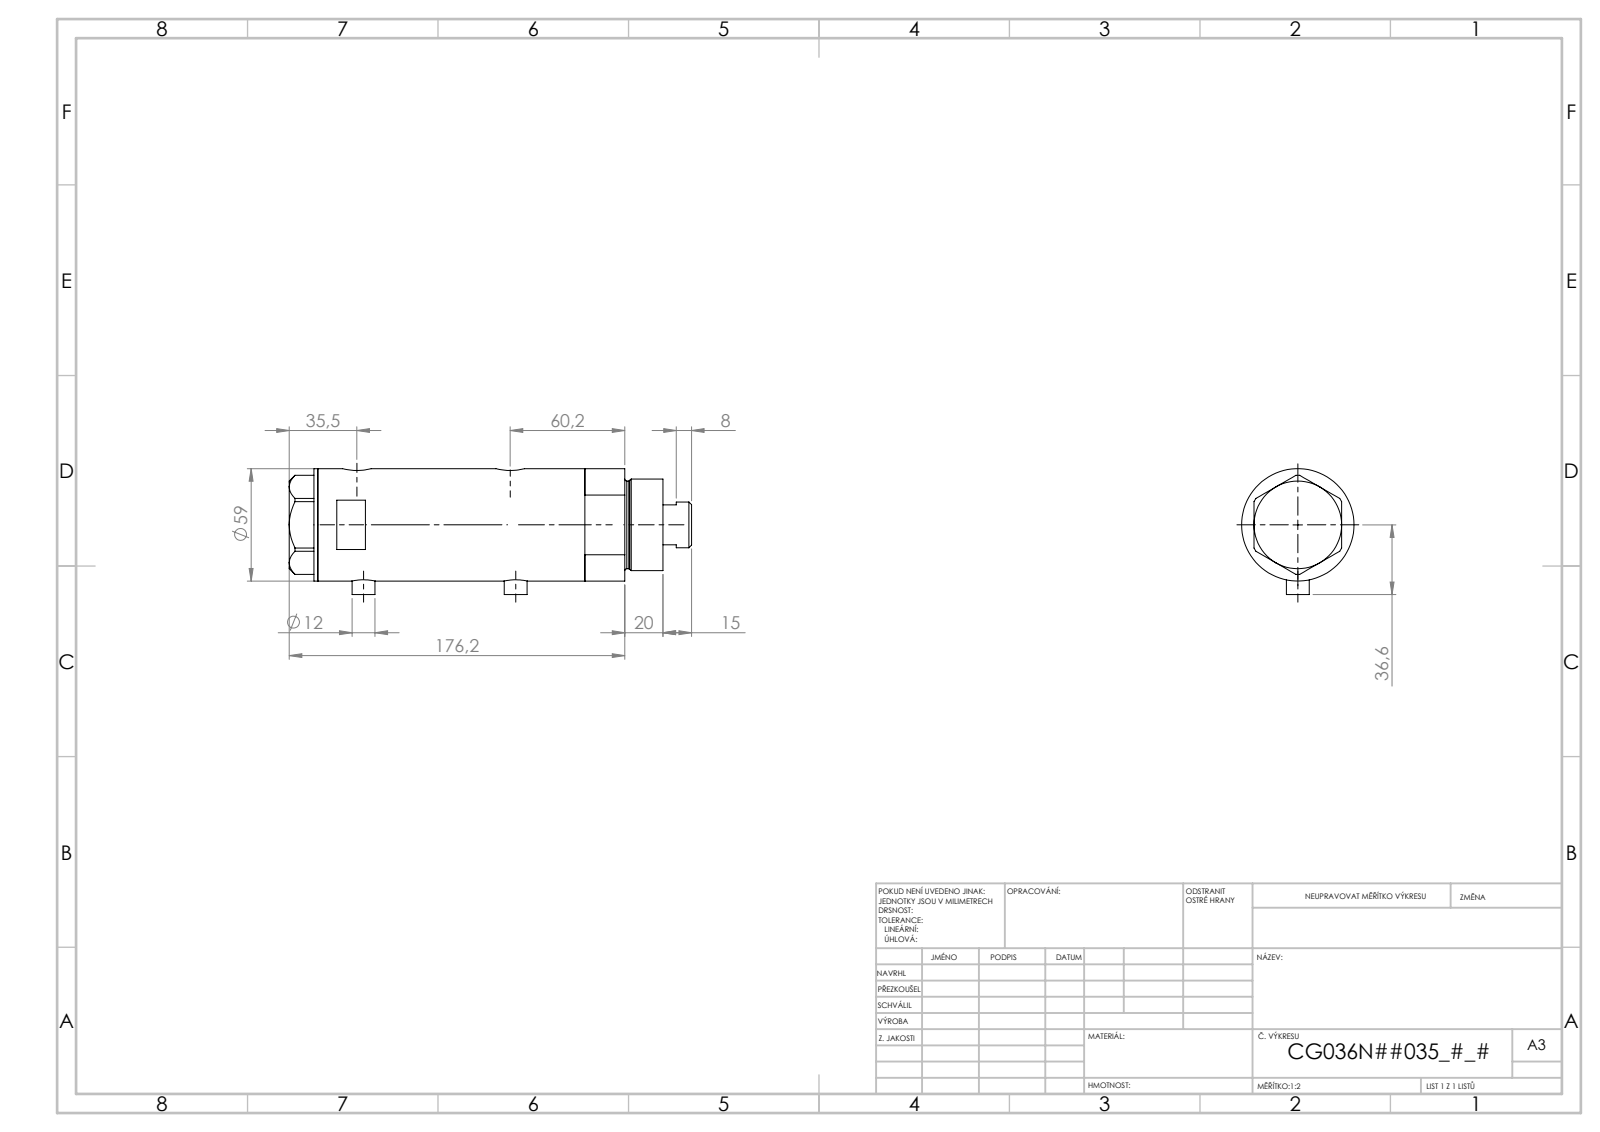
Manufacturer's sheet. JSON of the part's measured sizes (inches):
{"part_name": "V270CG_VC; V270CG_FRONT; V270CG_BACK; V270CG_MIDDLE", "step_written_by": "SolidWorks 2019 (CONFIG_CONTROL_DESIGN)", "units": "inches", "bodies": {"solids": 4, "faces": 126, "planar": 53, "cylindrical": 53, "other": 20}, "overall_size": [7.812, 2.366, 2.323], "volume_in3": 27.36, "surface_area_in2": 147.4, "round_holes": [[0.197, 2], [0.383, 2], [0.492, 2], [0.591, 2], [0.335, 1], [0.984, 1], [1.043, 1], [1.417, 1], [1.575, 1], [2.047, 1]], "round_bosses_or_shafts": [[0.472, 2], [2.323, 1], [1.89, 1], [1.811, 1], [0.945, 1]], "face_to_face_distances": [3.635, 0.925, 2.71, 0.591, 1.516, 4.226, 7.221, 6.631, 5.706, 2.995], "hole_center_spacings": [0.114, 0.138, 2.644, 2.758, 2.781, 2.896, 0.114, 0.115]}
